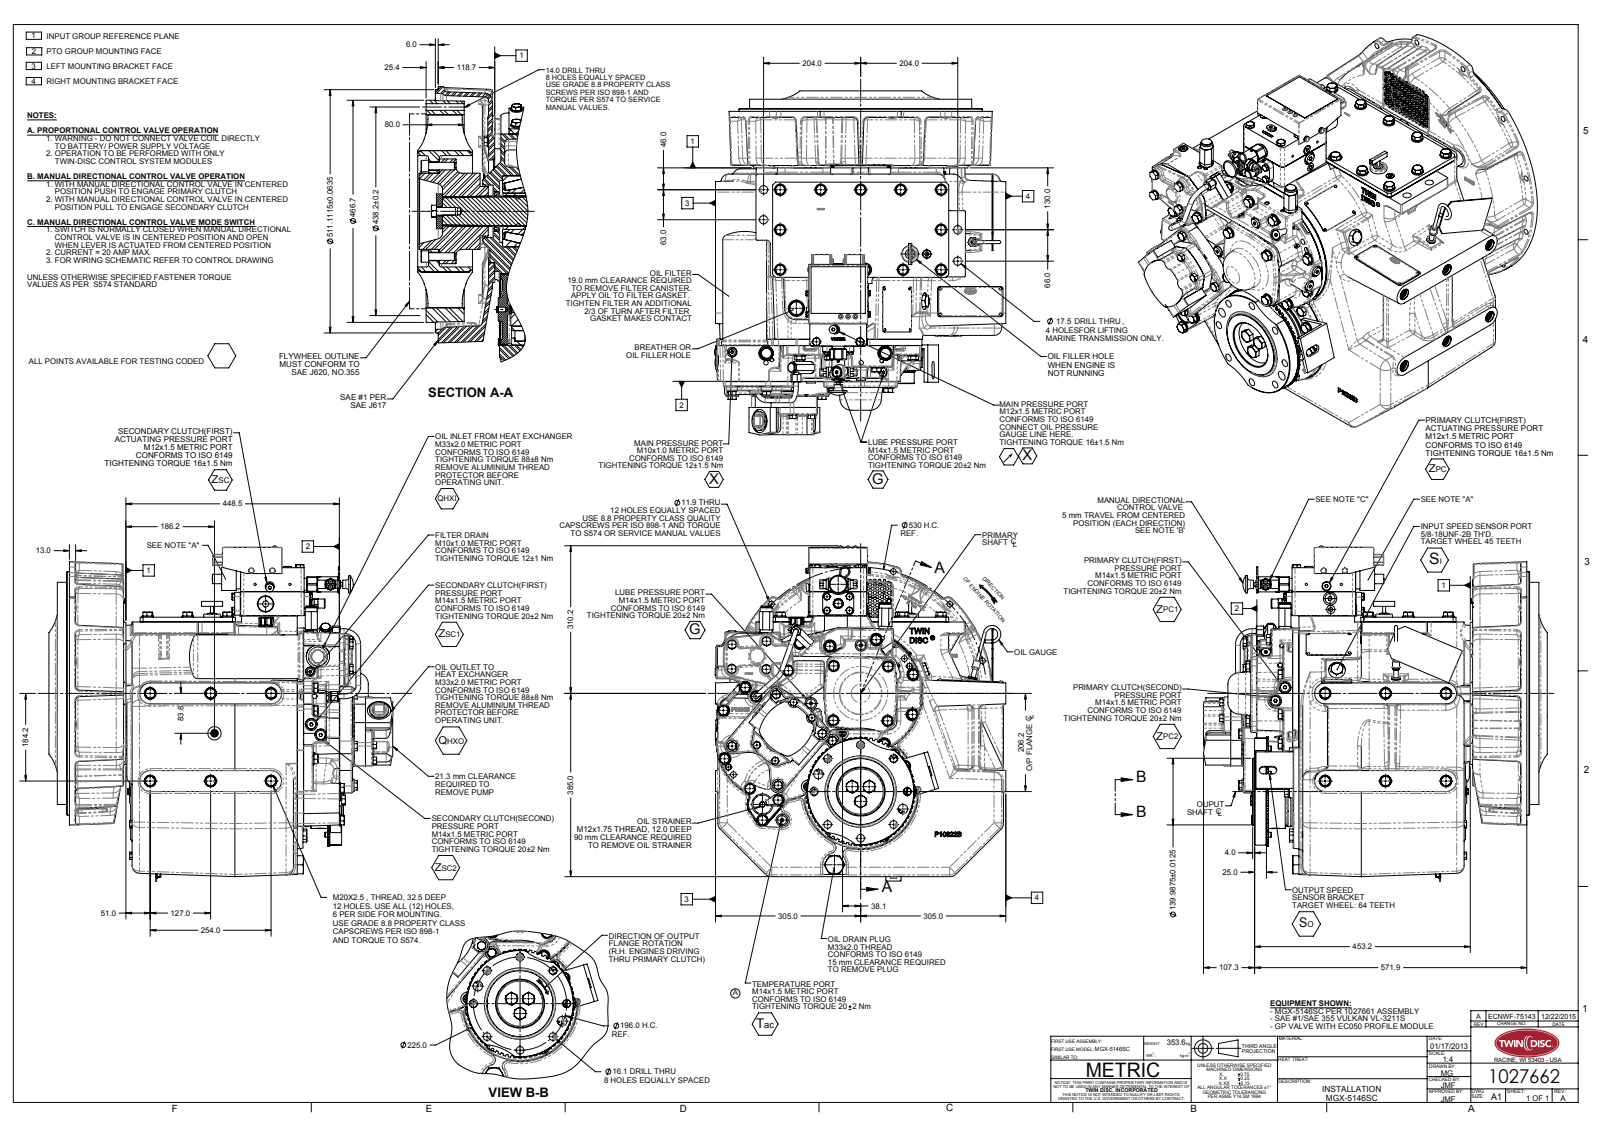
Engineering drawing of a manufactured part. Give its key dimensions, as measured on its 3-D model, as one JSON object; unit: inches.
{"part_name": "1027662", "step_written_by": "SolidWorks 2010 (AUTOMOTIVE_DESIGN)", "units": "inches", "bodies": {"solids": 0, "faces": 9282, "planar": 5569, "cylindrical": 1723, "other": 1990}, "overall_size": [35.214, 28.437, 26.736], "round_holes": [[0.276, 98], [0.469, 12], [0.984, 10], [0.551, 8], [0.634, 8], [0.787, 6], [0.926, 6], [0.368, 4], [0.472, 4], [0.689, 4], [0.189, 2], [0.304, 2]], "round_bosses_or_shafts": [[0.945, 47], [0.748, 8], [0.781, 5], [0.1, 5], [0.669, 4], [0.603, 4], [0.512, 4], [0.472, 3]], "partial_cylinders_radius": [[0.098, 88], [1.563, 72], [0.256, 60], [0.315, 60], [0.118, 51], [0.63, 32], [0.079, 23], [0.12, 23]], "face_to_face_distances": [0.015, 14.192, 14.177, 0.515, 0.531, 13.661, 2.953, 2.968, 3.483, 17.145], "hole_center_spacings": [0.394, 0.787, 18.073, 0.79, 1.181, 1.044, 1.365, 1.575]}
